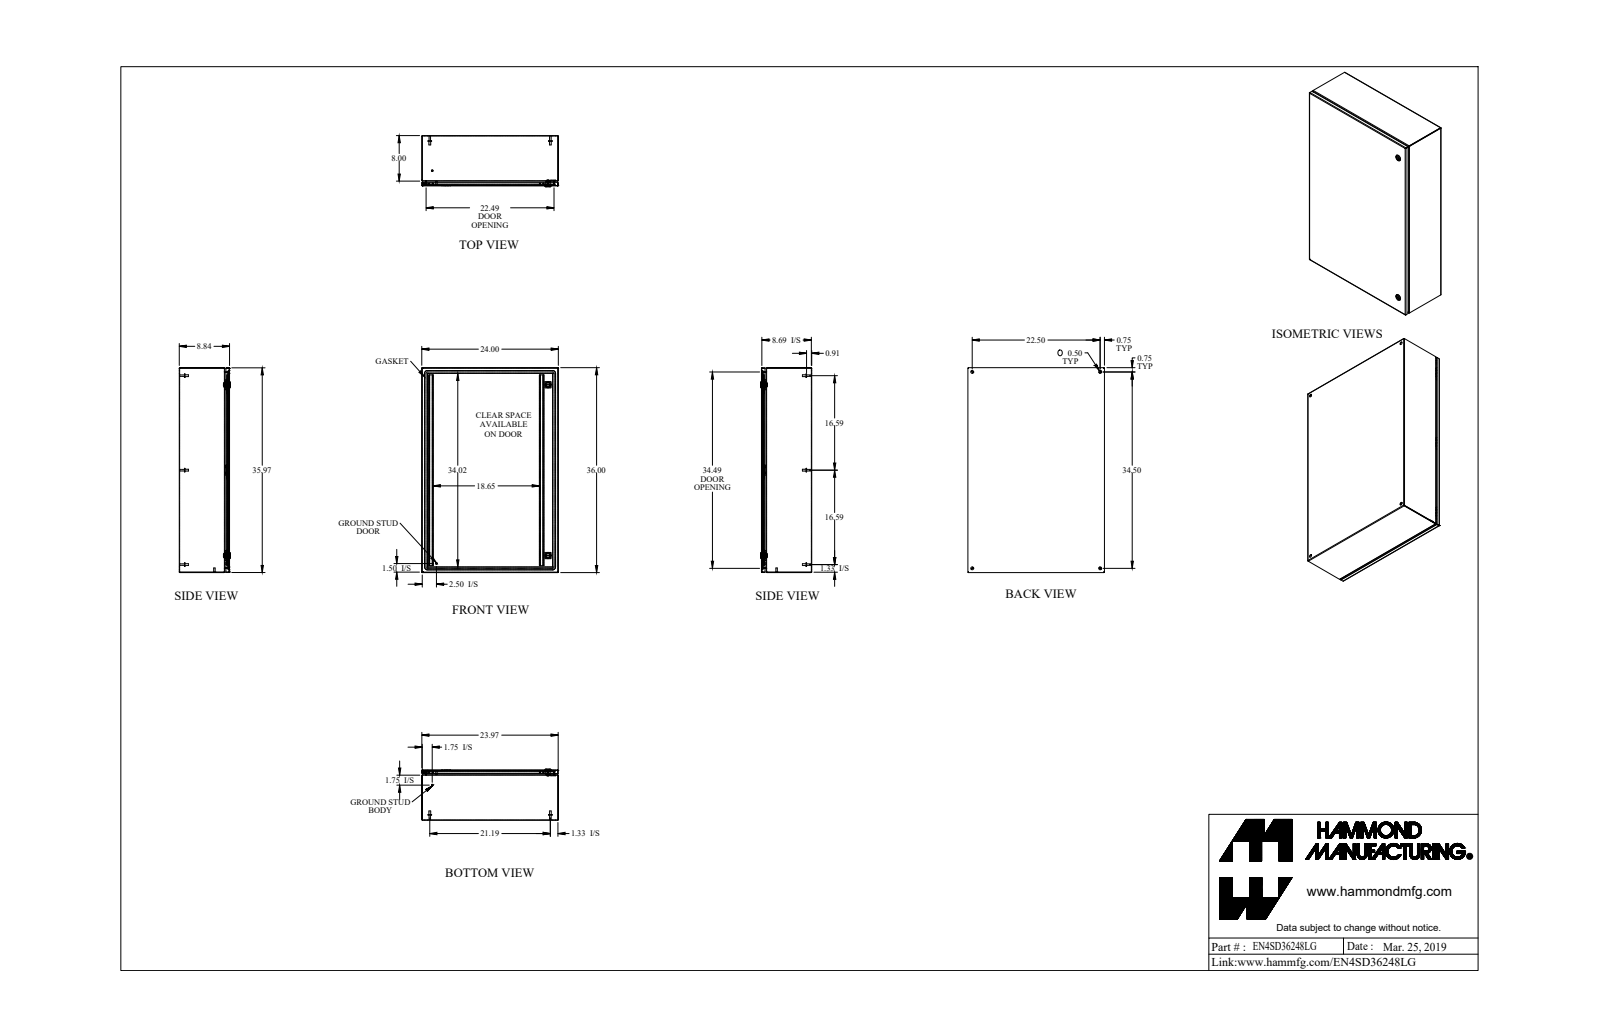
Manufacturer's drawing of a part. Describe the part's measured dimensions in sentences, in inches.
The part is named "EN4SD36248LG_Default". Its 3-D file was written by "SolidWorks 2019 (CONFIG_CONTROL_DESIGN)". It is 33 solids with 917 faces: 430 planar, 307 cylindrical and 180 other. Overall it measures 36 by 24 by 8.997 inches. Its volume is 226.9 cubic inches and its surface area 6 373 square inches. Round holes: 4 of diameter 0.5, 2 of diameter 0.232, 2 of diameter 0.625, 2 of diameter 0.785, 1 of diameter 0.172, 1 of diameter 0.24, 1 of diameter 0.242. Round bosses or shafts: 6 of diameter 0.625, 6 of diameter 0.313, 6 of diameter 0.27, 2 of diameter 1.1, 2 of diameter 0.525, 2 of diameter 0.281, 2 of diameter 0.25, 1 of diameter 0.455. Partial cylindrical surfaces (rounded edges, fillets, slot ends): 20 of radius 0.036, 20 of radius 0.108, 12 of radius 0.043, 12 of radius 0.081, 12 of radius 0.382, 8 of radius 19.003, 6 of radius 0.006, 6 of radius 0.062. The main face-to-face distances are 0.072, 8.765, 8.693, 8.837, 23.928, 35.928, 23.856, 24, 35.856, 36. The hole center spacings are 22.5, 34.5, 41.189, 2.493, 2.494, 21.545, 21.545, 29.999.
